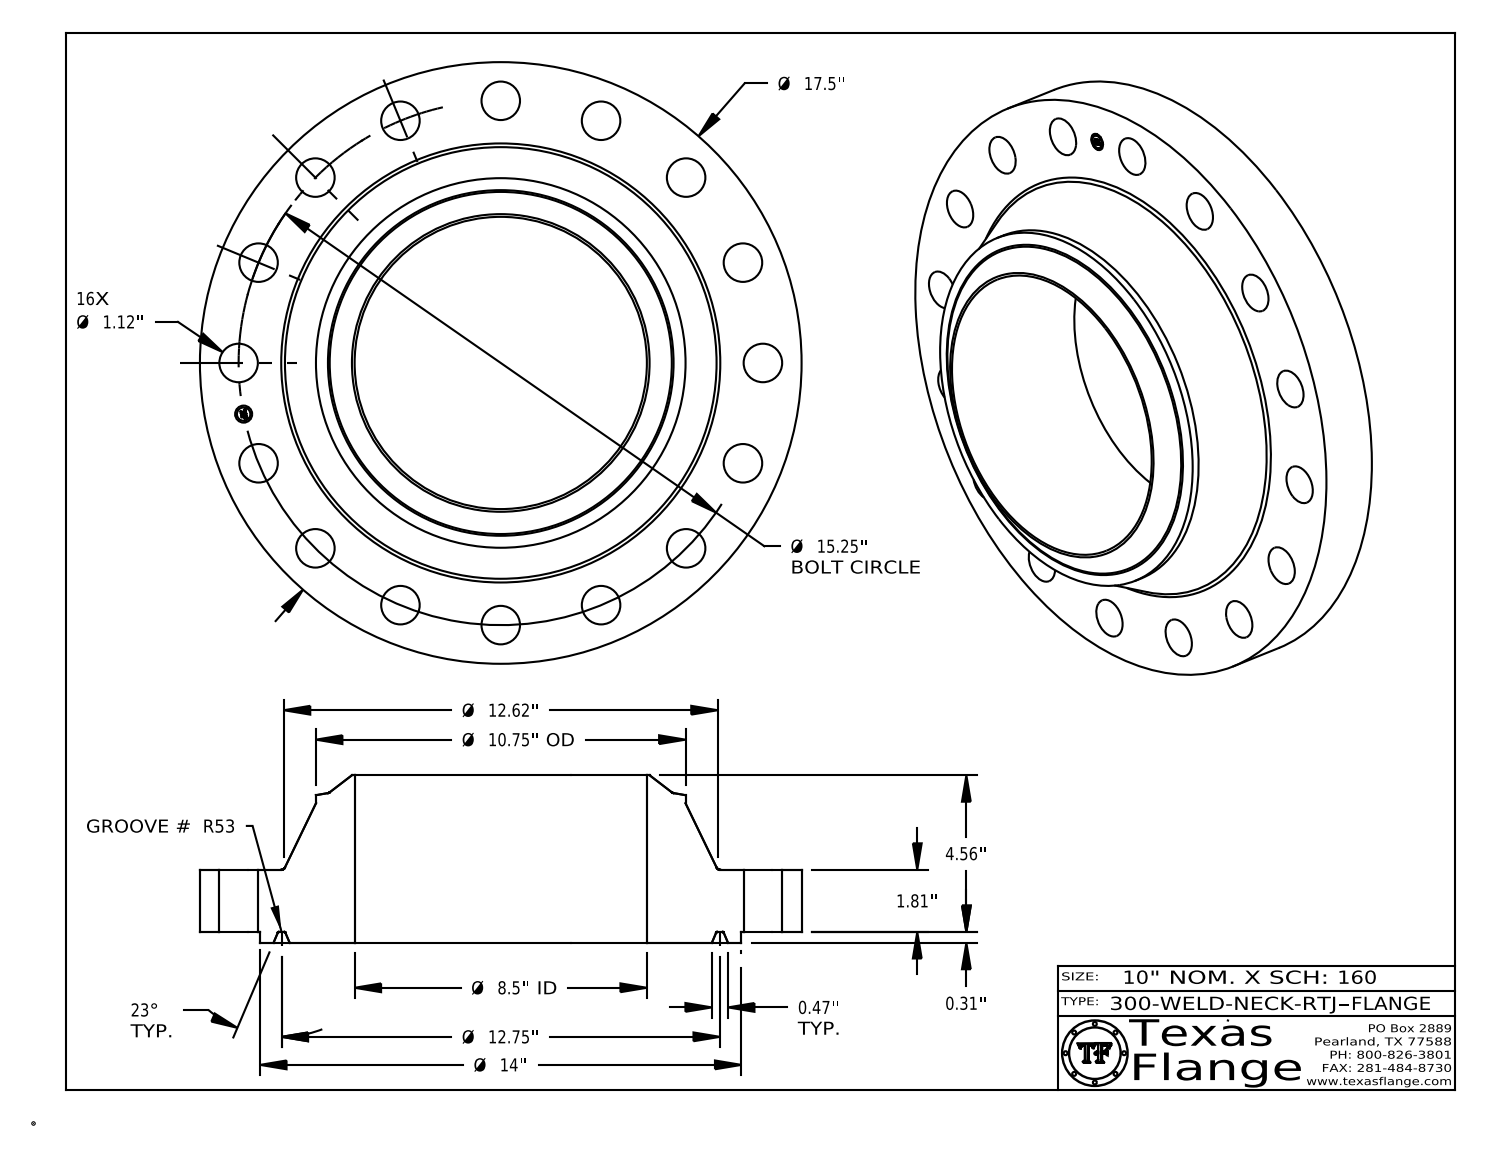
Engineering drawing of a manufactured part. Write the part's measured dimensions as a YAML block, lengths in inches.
part_name: "300-WELD-NECK-RTJ"
step_written_by: "CATIA V5 STEP AP214 (AUTOMOTIVE_DESIGN)"
units: inches
bodies: {solids: 1, faces: 449, planar: 371, cylindrical: 60, other: 18}
overall_size: [17.5, 17.5, 4.873]
volume: 444.3
surface_area: 754.8
round_holes:
  - {diameter: 1.12, count: 16}
  - {diameter: 0.495, count: 1}
  - {diameter: 8.5, count: 1}
round_bosses_or_shafts:
  - {diameter: 0.03, count: 8}
  - {diameter: 17.5, count: 1}
  - {diameter: 14, count: 1}
  - {diameter: 10.75, count: 1}
  - {diameter: 0.39, count: 1}
face_to_face_distances: [2.123, 0.313, 1.81, 4.873, 4.56, 2.75, 0.015, 2.108, 1.795, 2.765]
hole_center_spacings: [8.472, 10.783, 14.957, 14.089, 7.625, 2.975, 2.975, 5.836]
